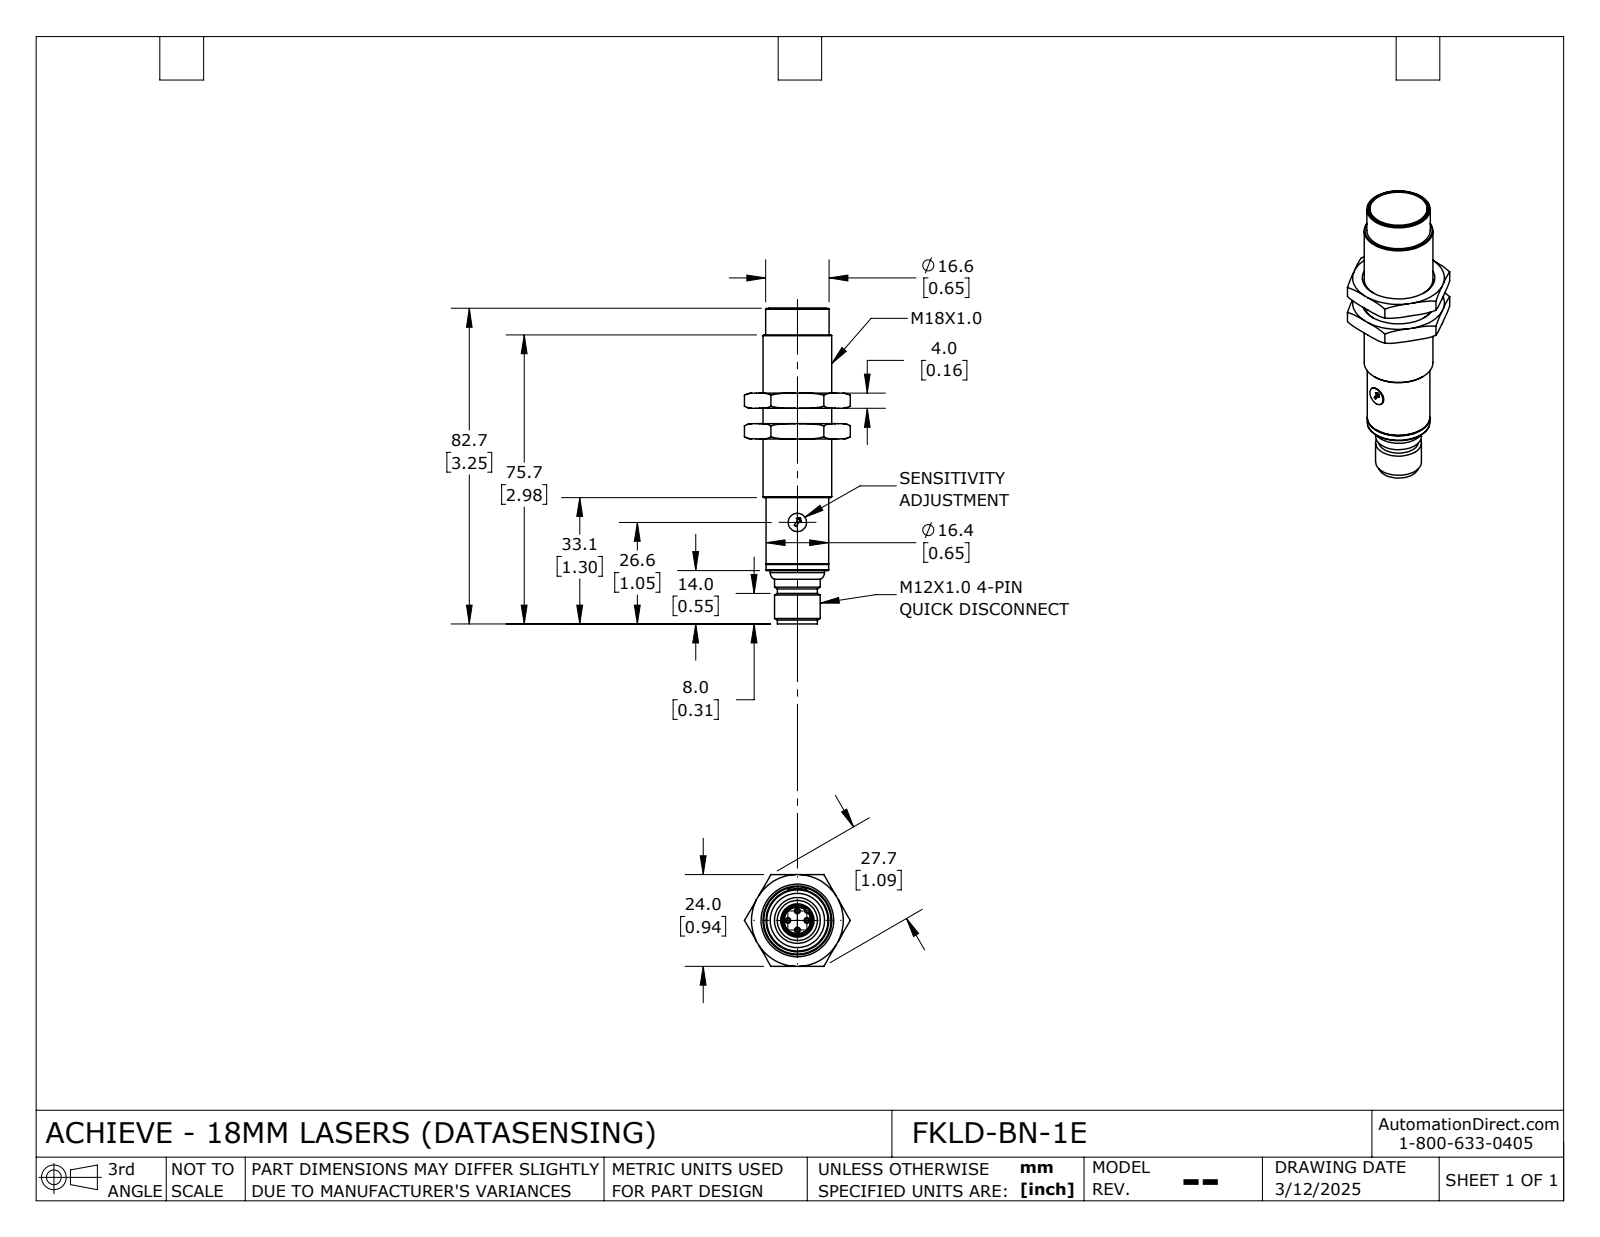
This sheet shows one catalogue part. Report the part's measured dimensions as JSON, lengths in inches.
{"part_name": "FKLD-BN-1E_Default", "step_written_by": "SolidWorks 2024 (CONFIG_CONTROL_DESIGN)", "units": "inches", "bodies": {"solids": 3, "faces": 127, "planar": 48, "cylindrical": 30, "other": 49}, "overall_size": [3.254, 1.091, 0.945], "volume_in3": 1.176, "surface_area_in2": 12.63, "round_holes": [[0.278, 1], [0.327, 1], [0.587, 1], [0.709, 1]], "round_bosses_or_shafts": [[0.039, 4], [0.654, 1], [0.646, 1], [0.591, 1], [0.583, 1], [0.559, 1], [0.472, 1], [0.413, 1]], "partial_cylinders_radius": [[0.02, 2], [0.297, 2], [0.024, 1], [0.053, 1]], "face_to_face_distances": [0.157, 0.315, 0.945, 0.093, 0.1, 1.088, 1.096, 1.189, 0.773, 0.781]}
